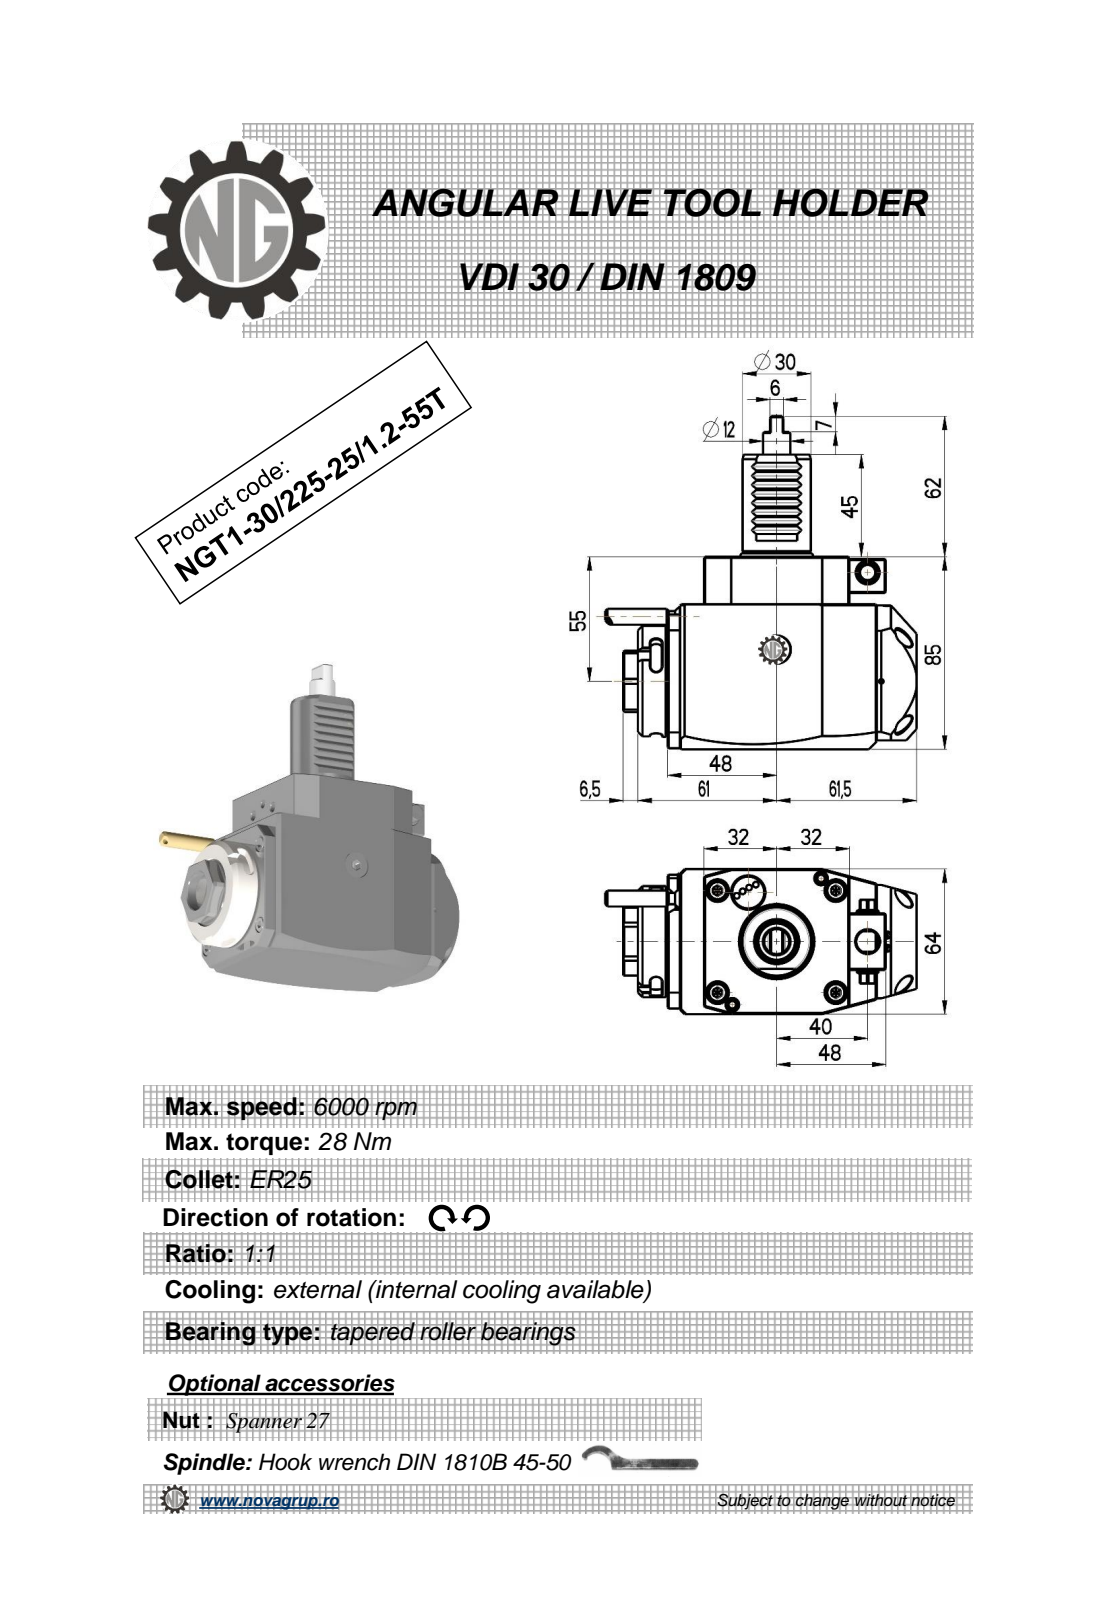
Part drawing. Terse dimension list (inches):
name: NGT1_30_225_25_1_2_55T
written by: PRO/ENGINEER BY PARAMETRIC TECHNOLOGY CORPORATION, 2010280 (CONFIG_CONTROL_DESIGN)
unit: in
bodies: 1 solid, 337 faces (183 planar, 84 cylindrical, 70 other)
size: 5.787 × 5.389 × 2.52
volume: 33.46 in³; area: 76.06 in²
holes: 1× ⌀0.098, 1× ⌀0.118, 1× ⌀0.374, 1× ⌀0.394, 1× ⌀0.709
bosses: 2× ⌀0.315, 1× ⌀1.929, 1× ⌀1.654, 1× ⌀1.181, 1× ⌀0.472, 1× ⌀0.394, 1× ⌀0.276, 1× ⌀0.197
rounds: 8× R0.012, 6× R0.098, 2× R0.031, 2× R7.087, 1× R0.152, 1× R0.167, 1× R0.177, 1× R0.591
face distances: 2.52, 3.346, 0.63, 3.15, 4.311, 0.512, 0.827, 1.142, 4.823, 3.681
hole spacings: 1.03, 1.348, 1.831
